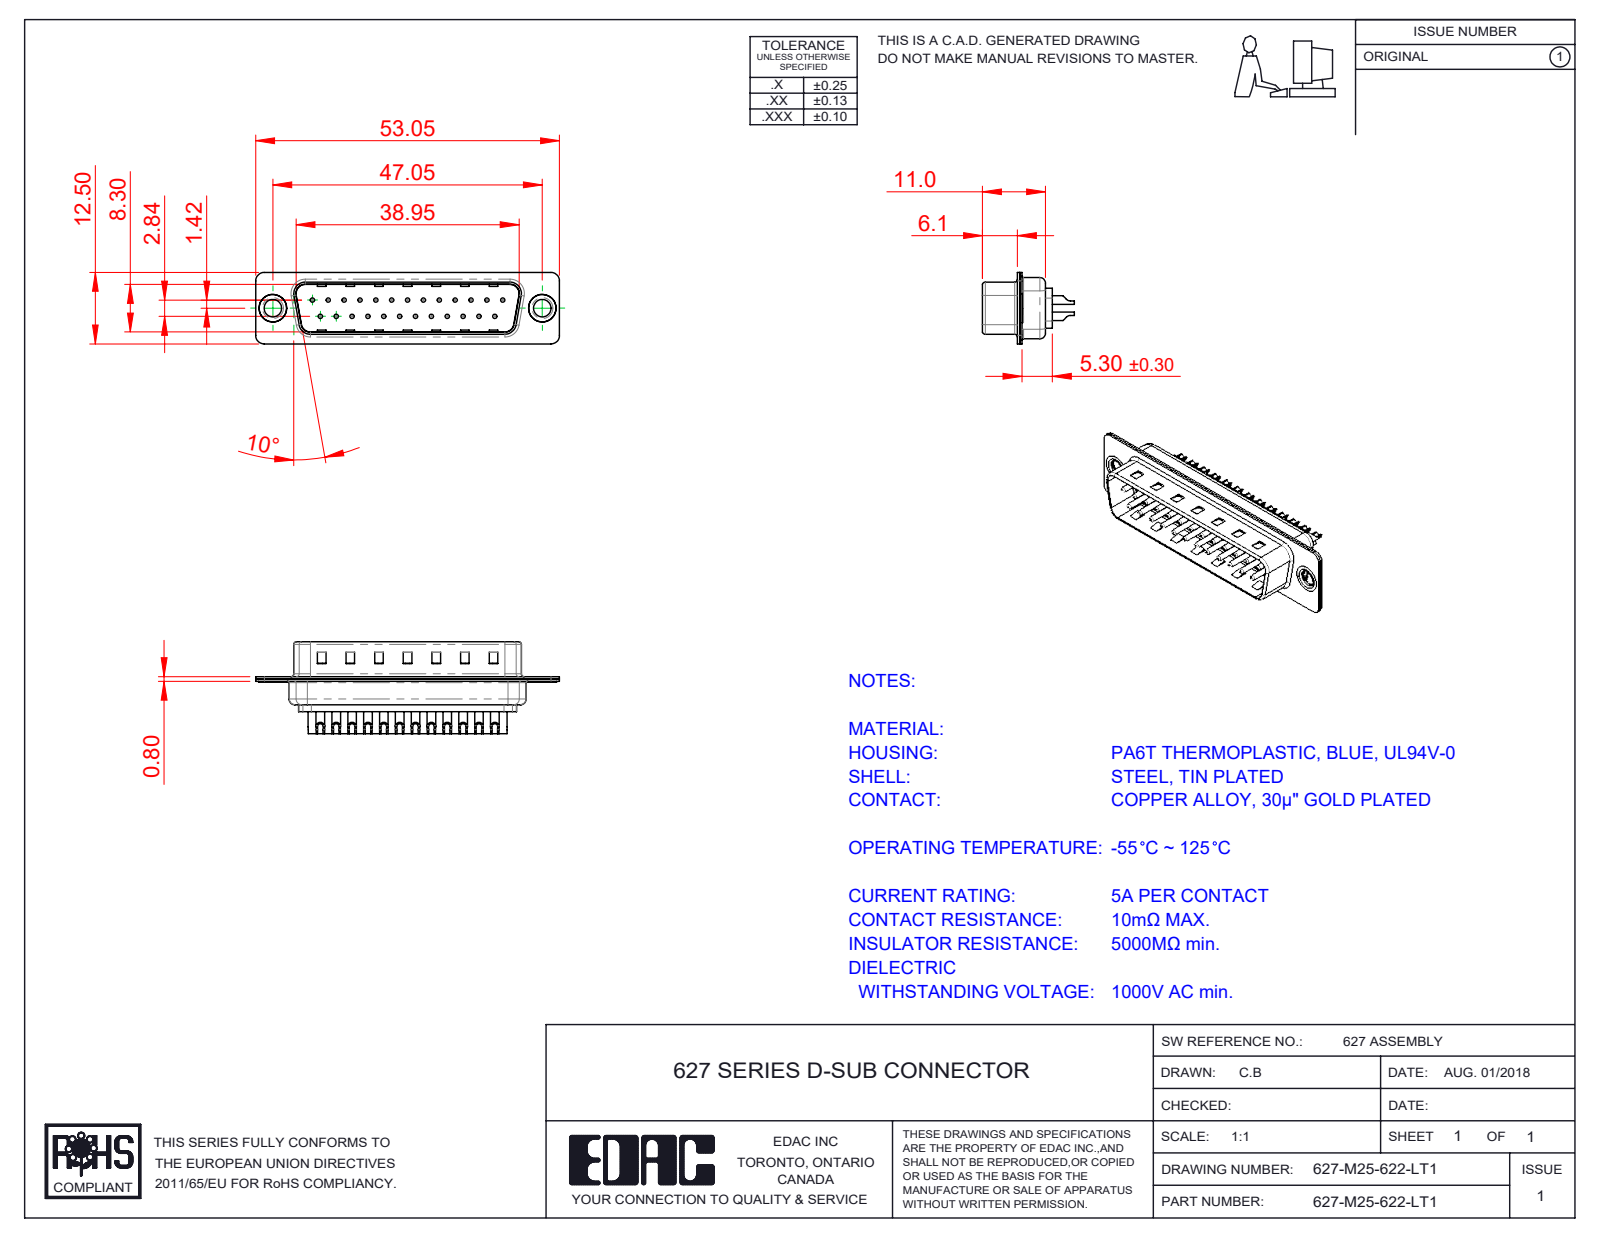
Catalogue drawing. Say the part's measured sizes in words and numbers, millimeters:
The part is named "627M Shell Front_25 Contacts; 627M Contact Row 2_22; 627M Housing_25 Contacts; 627M Shell Rear_25 Contacts (+3 more)". Its 3-D file was written by "SolidWorks 2020 (CONFIG_CONTROL_DESIGN)". It is 30 solids with 1275 faces: 396 planar, 521 cylindrical and 358 other. Overall it measures 53.05 by 16.05 by 12.5 millimeters. Its volume is 2 698 cubic millimeters and its surface area 6 932 square millimeters. Round holes: 25 of diameter 0.75, 25 of diameter 1, 25 of diameter 1.6, 25 of diameter 2, 2 of diameter 3.05, 2 of diameter 4, 2 of diameter 4.8. Round bosses or shafts: 25 of diameter 1.5, 2 of diameter 5, 2 of diameter 4.9, 2 of diameter 3.55. Partial cylindrical surfaces (rounded edges, fillets, slot ends): 16 of radius 1.5, 12 of radius 2, 8 of radius 0.5, 8 of radius 1.6, 6 of radius 1, 4 of radius 0.25, 4 of radius 0.6, 4 of radius 0.65. The main face-to-face distances are 0.4, 0.8, 9.5, 9.1, 8.7, 9.9, 1.2, 0.75, 0.35, 6.1. The hole center spacings are 3.16, 2.77, 5.54, 8.31, 11.08, 13.85, 16.62, 5.03.
